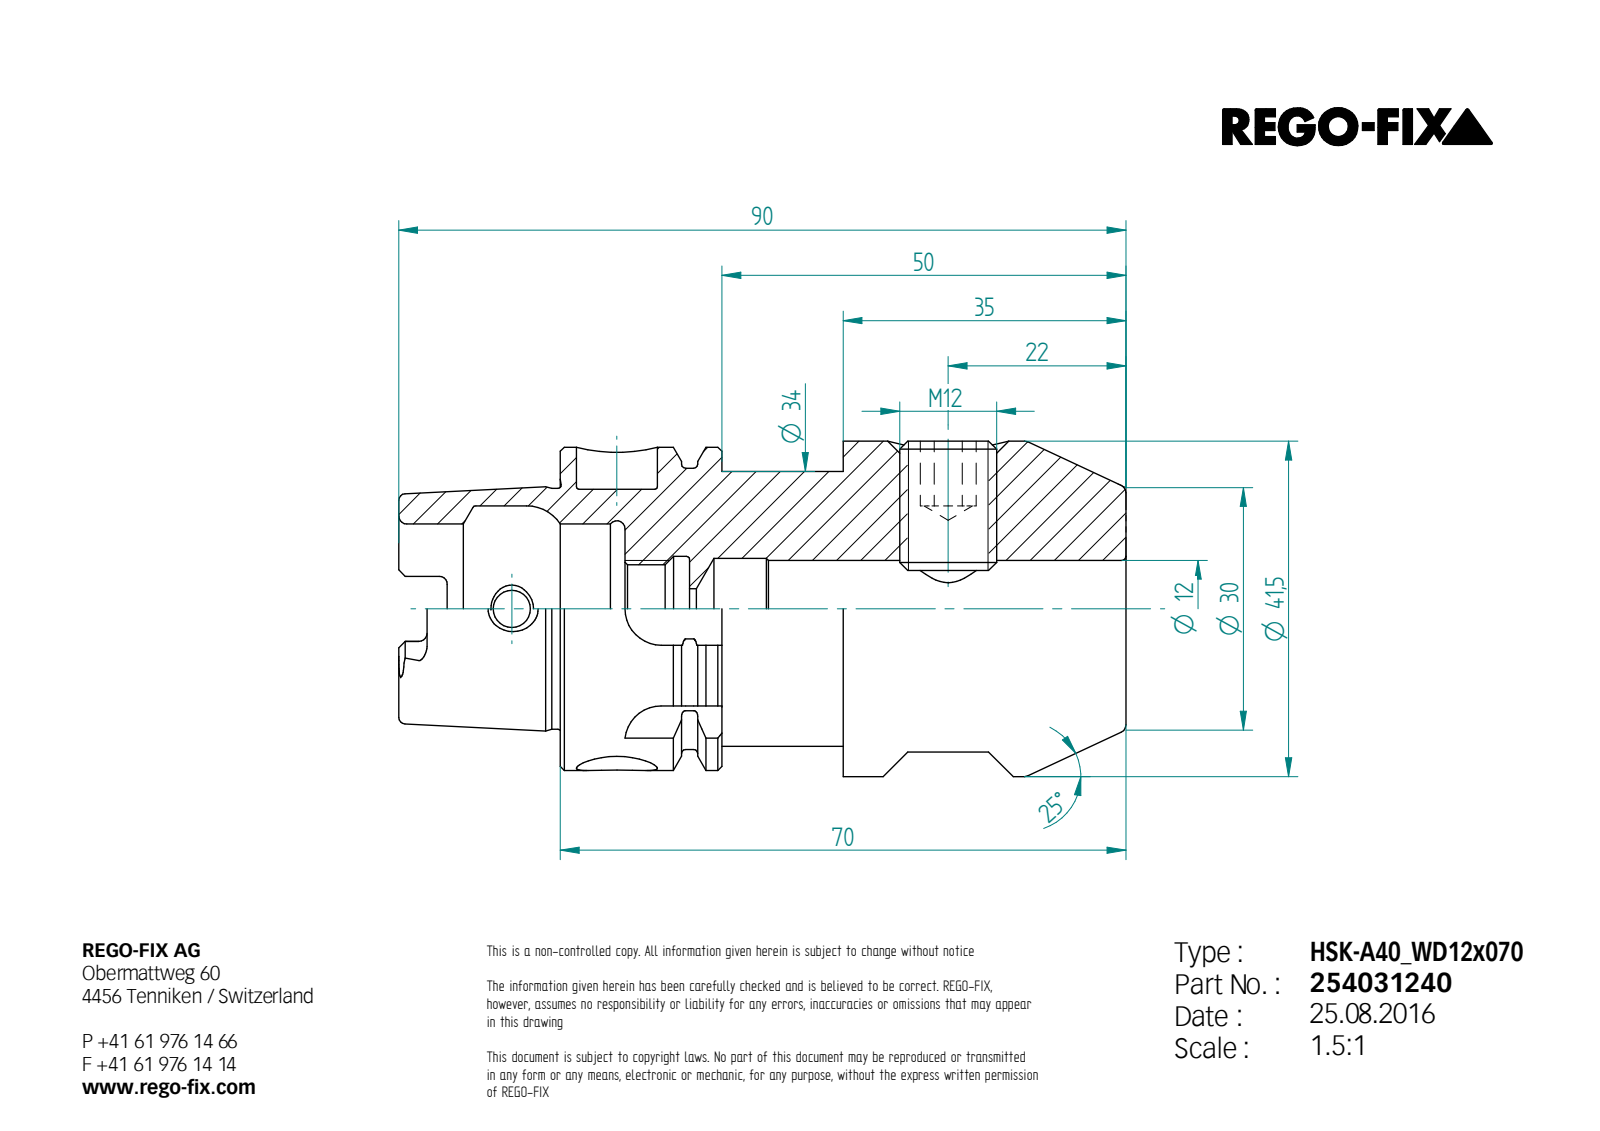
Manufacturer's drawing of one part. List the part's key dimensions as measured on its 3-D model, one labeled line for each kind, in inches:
STEP written by: Unknown (AUTOMOTIVE_DESIGN)
Units: inches
Bodies: 2 solids, 158 faces (65 planar, 38 cylindrical, 55 other)
Overall size (bounding box): 3.543 × 1.634 × 1.634
Volume: 4.534 in³ · Surface area: 29.71 in²
Round holes (diameter × count): ⌀0.394 ×2, ⌀0.181 ×1, ⌀0.197 ×1, ⌀0.398 ×1, ⌀0.43 ×1, ⌀0.472 ×1, ⌀0.492 ×1, ⌀0.512 ×1, ⌀0.827 ×1, ⌀1.004 ×1
Round bosses / shafts (diameter × count): ⌀1.634 ×1, ⌀1.575 ×1, ⌀1.37 ×1, ⌀1.339 ×1, ⌀1.173 ×1, ⌀0.472 ×1
Partial cylindrical surfaces — rounded edges, fillets, slot ends (radius × count): R0.039 ×6, R0.074 ×4, R0.177 ×4
Main face-to-face distances: 1.378, 0.787, 2.756, 0.315, 0.591, 1.969, 0.472, 1.063, 2.441, 0.63
Hole centre spacings: 1.614
